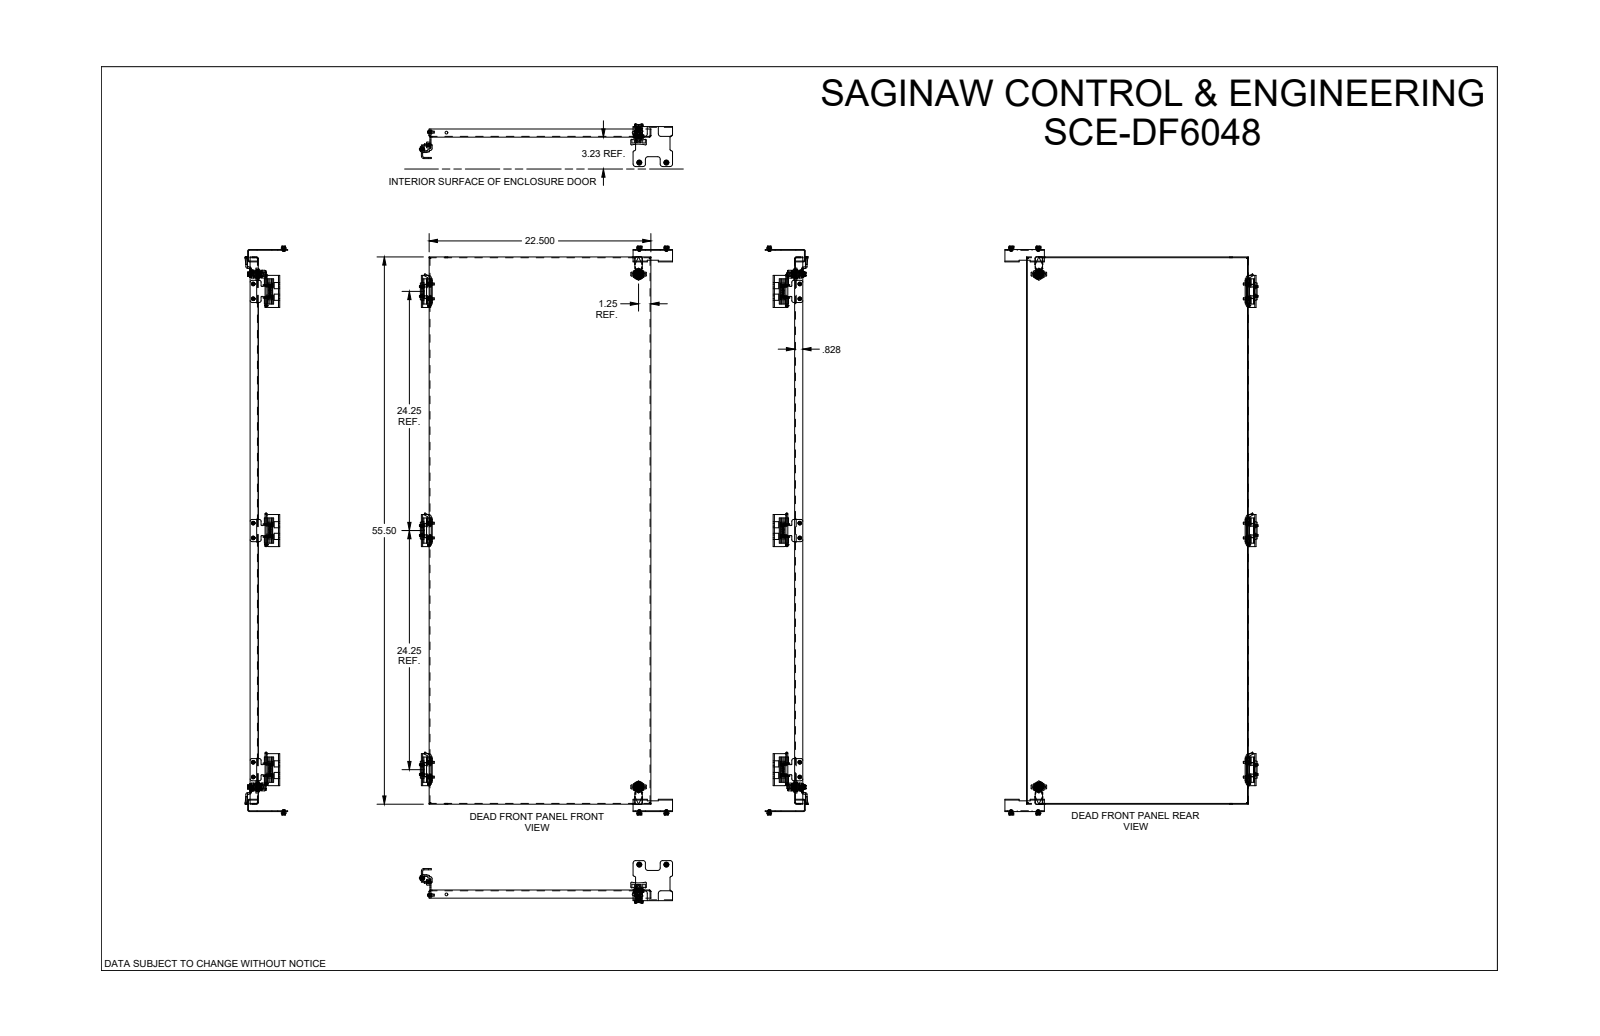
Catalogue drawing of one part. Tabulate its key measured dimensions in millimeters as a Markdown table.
| quantity | value |
| --- | --- |
| part name | SCE-DF6048 |
| STEP written by | SolidWorks 2021 (AUTOMOTIVE_DESIGN) |
| units | millimeters |
| bodies | 56 solids, 2317 faces (1122 planar, 676 cylindrical, 519 other) |
| overall size | 1465.3 × 652.2 × 109.7 |
| volume | 1 539 000 mm³ |
| surface area | 1 934 000 mm² |
| round holes (diameter × count) | 4.8 × 8, 4.4 × 6, 5.3 × 6, 6.2 × 6, 6.4 × 6, 6.8 × 6, 5 × 2, 8 × 2, 10 × 2, 11 × 2, 16.1 × 2, 5.6 × 1 |
| round bosses / shafts (diameter × count) | 4.3 × 8, 9.5 × 6, 8.6 × 6, 6.4 × 6, 6.3 × 6, 4.8 × 6, 5 × 4, 28 × 2 |
| partial cylindrical surfaces (radius × count) | 0.3 × 56, 6.4 × 23, 0.5 × 22, 4 × 16, 1.6 × 14, 0.3 × 13, 1.7 × 9, 3.2 × 9 |
| main face-to-face distances | 1.5, 570, 2, 571.5, 568.5, 1408.2, 17.1, 18.6, 1425.2, 1426.8 |
| hole center spacings | 616, 25, 44.4, 44.5, 54.1, 54.1, 1231.9, 586 |
